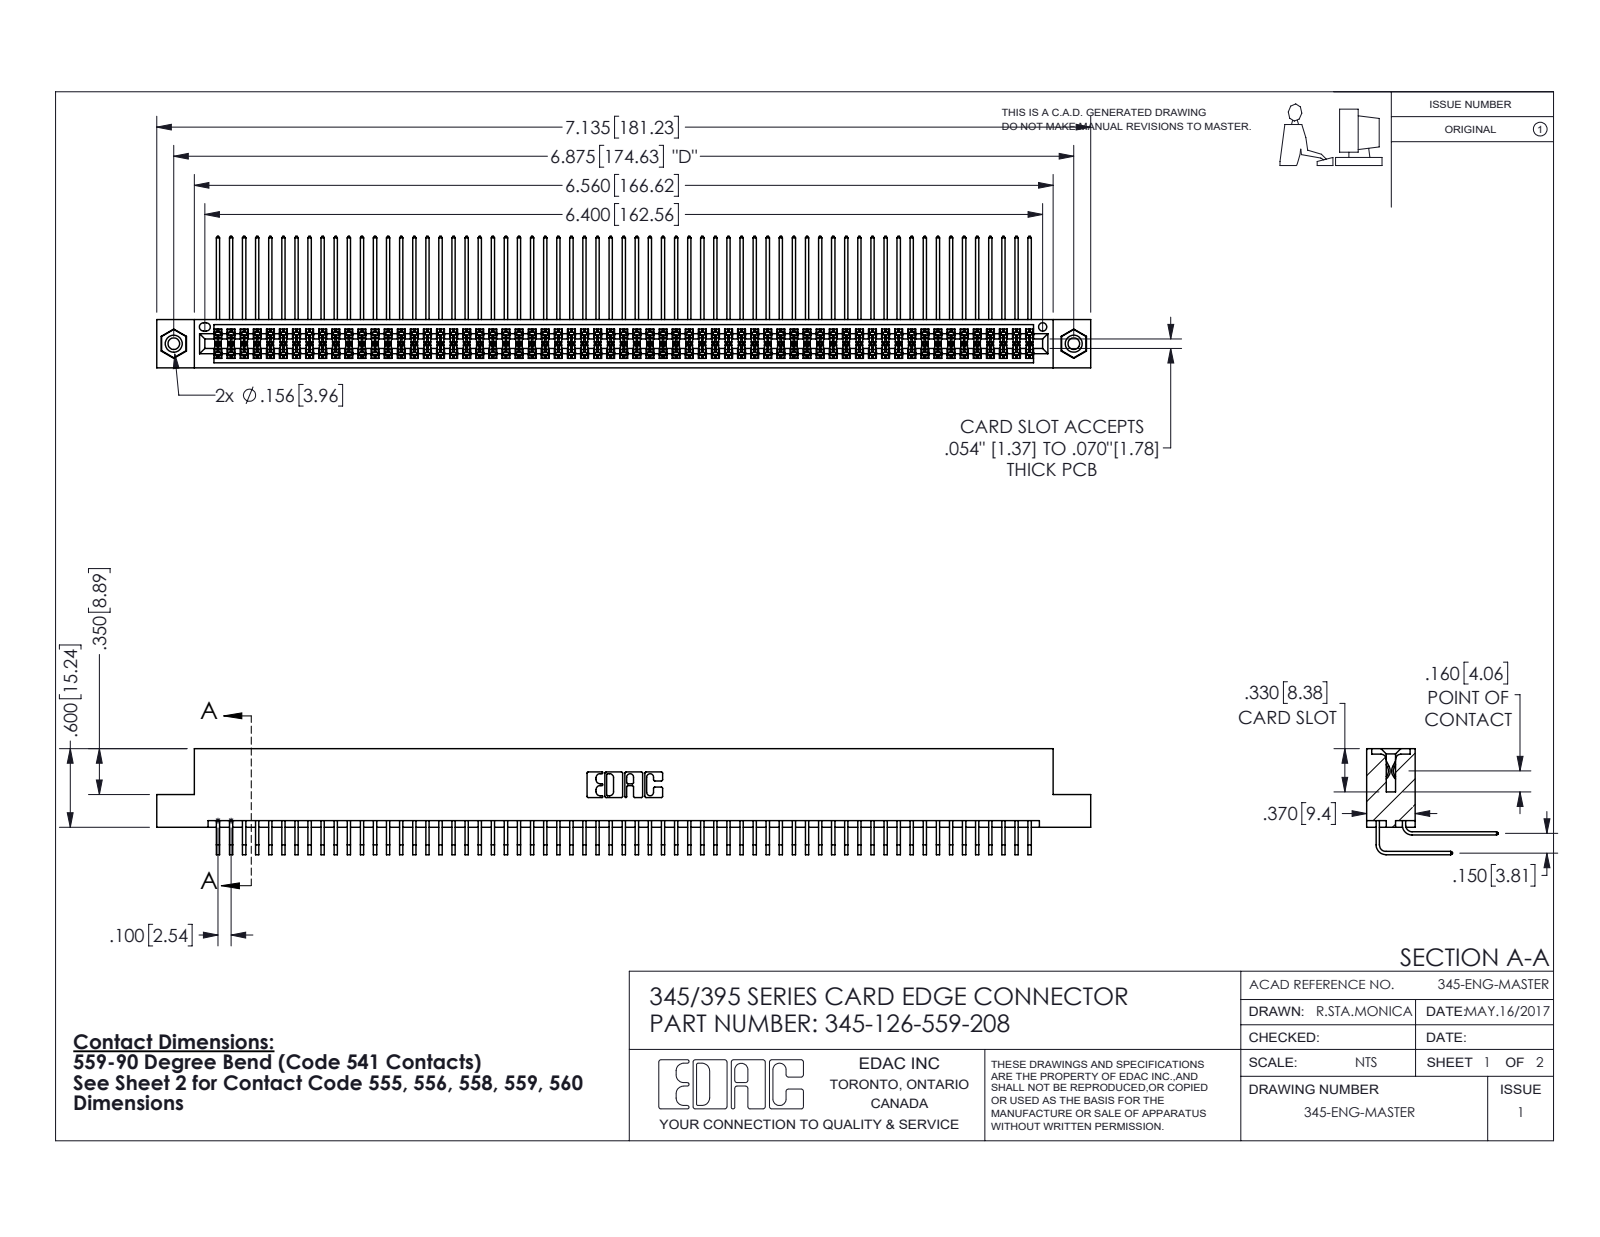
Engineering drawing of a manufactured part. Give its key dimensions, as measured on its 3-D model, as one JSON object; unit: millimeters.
{"part_name": "345-250-001_345-250-003-102; 345-126-559-208; 345-292-001_559 Tail - 2; 345-292-001_558 559 Tail - 1 (+1 more)", "step_written_by": "SolidWorks 2016 (CONFIG_CONTROL_DESIGN)", "units": "millimeters", "bodies": {"solids": 129, "faces": 6738, "planar": 4522, "cylindrical": 2200, "other": 16}, "overall_size": [181.2, 25.5, 20.5], "volume_mm3": 18520, "surface_area_mm2": 31210, "round_holes": [[2.3, 2], [3.2, 2], [4, 2], [1.6, 1]], "round_bosses_or_shafts": [[3.9, 2]], "partial_cylinders_radius": [[0.2, 251], [0.3, 22], [0.2, 6], [0.8, 6], [0.7, 3], [0.4, 2], [0.5, 2], [0.6, 2]], "face_to_face_distances": [1.8, 7.6, 5.1, 9.4, 2.5, 6.9, 0.6, 5.7, 4.4, 3.8], "hole_center_spacings": [6.9, 168.6, 174.6]}
